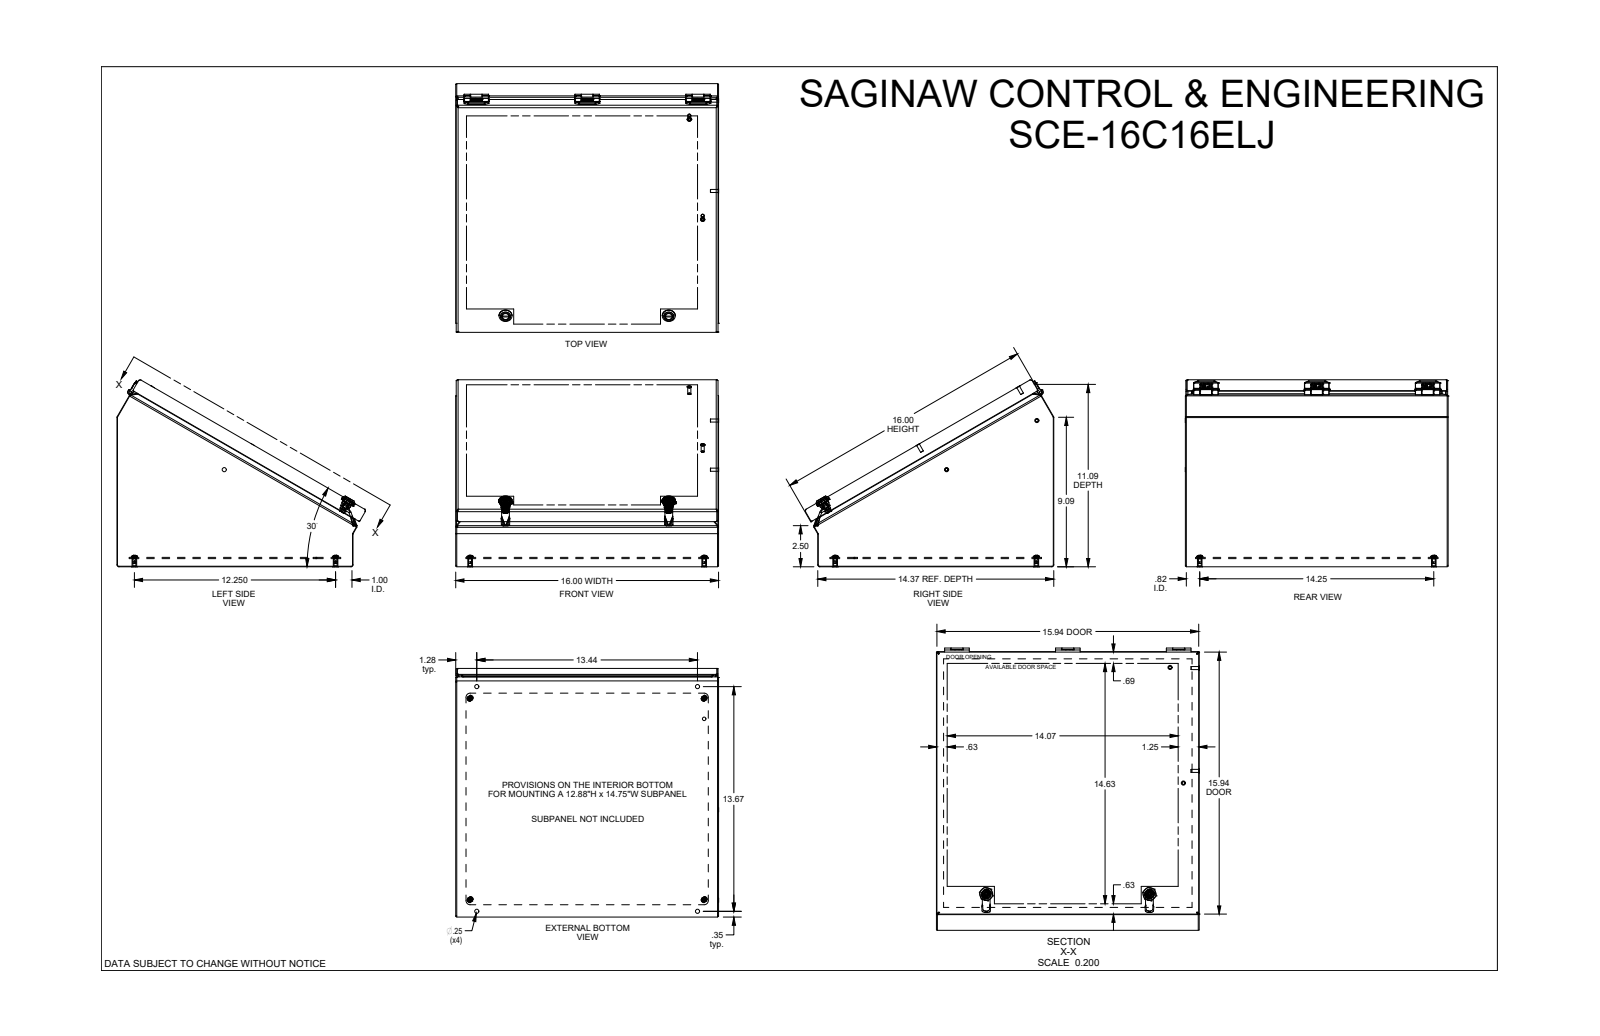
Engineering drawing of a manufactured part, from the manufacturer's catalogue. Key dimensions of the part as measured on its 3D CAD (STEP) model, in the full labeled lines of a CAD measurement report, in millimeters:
Part name (STEP PRODUCT): SCE-16C16ELJ
STEP written by: SolidWorks 2019 (AUTOMOTIVE_DESIGN)
Units: millimetres
Bodies: 35 solids, 1332 faces (515 planar, 541 cylindrical, 276 other)
Overall size (bounding box): 406.5 × 384.3 × 289.1
Volume: 1 298 000 mm³ · Surface area: 1 604 000 mm²
Round holes (diameter × count): ⌀6.4 ×8, ⌀4.8 ×4, ⌀4.9 ×4, ⌀7.1 ×4, ⌀0.5 ×3, ⌀2.5 ×3, ⌀4.4 ×3, ⌀6.8 ×3, ⌀5.1 ×2, ⌀6.1 ×2, ⌀6.5 ×2, ⌀6.8 ×2
Round bosses / shafts (diameter × count): ⌀7.1 ×4, ⌀6.5 ×4, ⌀4.8 ×4, ⌀6.6 ×3, ⌀4.6 ×3, ⌀20 ×2, ⌀13.9 ×2, ⌀11.7 ×2
Partial cylindrical surfaces — rounded edges, fillets, slot ends (radius × count): R0.8 ×36, R0.3 ×31, R1.5 ×24, R0.3 ×22, R0.4 ×22, R3 ×16, R0.5 ×13, R1.6 ×10
Main face-to-face distances: 1.5, 404.9, 1.9, 11.1, 12.6, 13, 14.5, 1.5, 403.4, 406.4
Hole centre spacings: 20.8, 171.5, 329.3, 352.1, 481.7, 311.2, 341.3, 342.9
